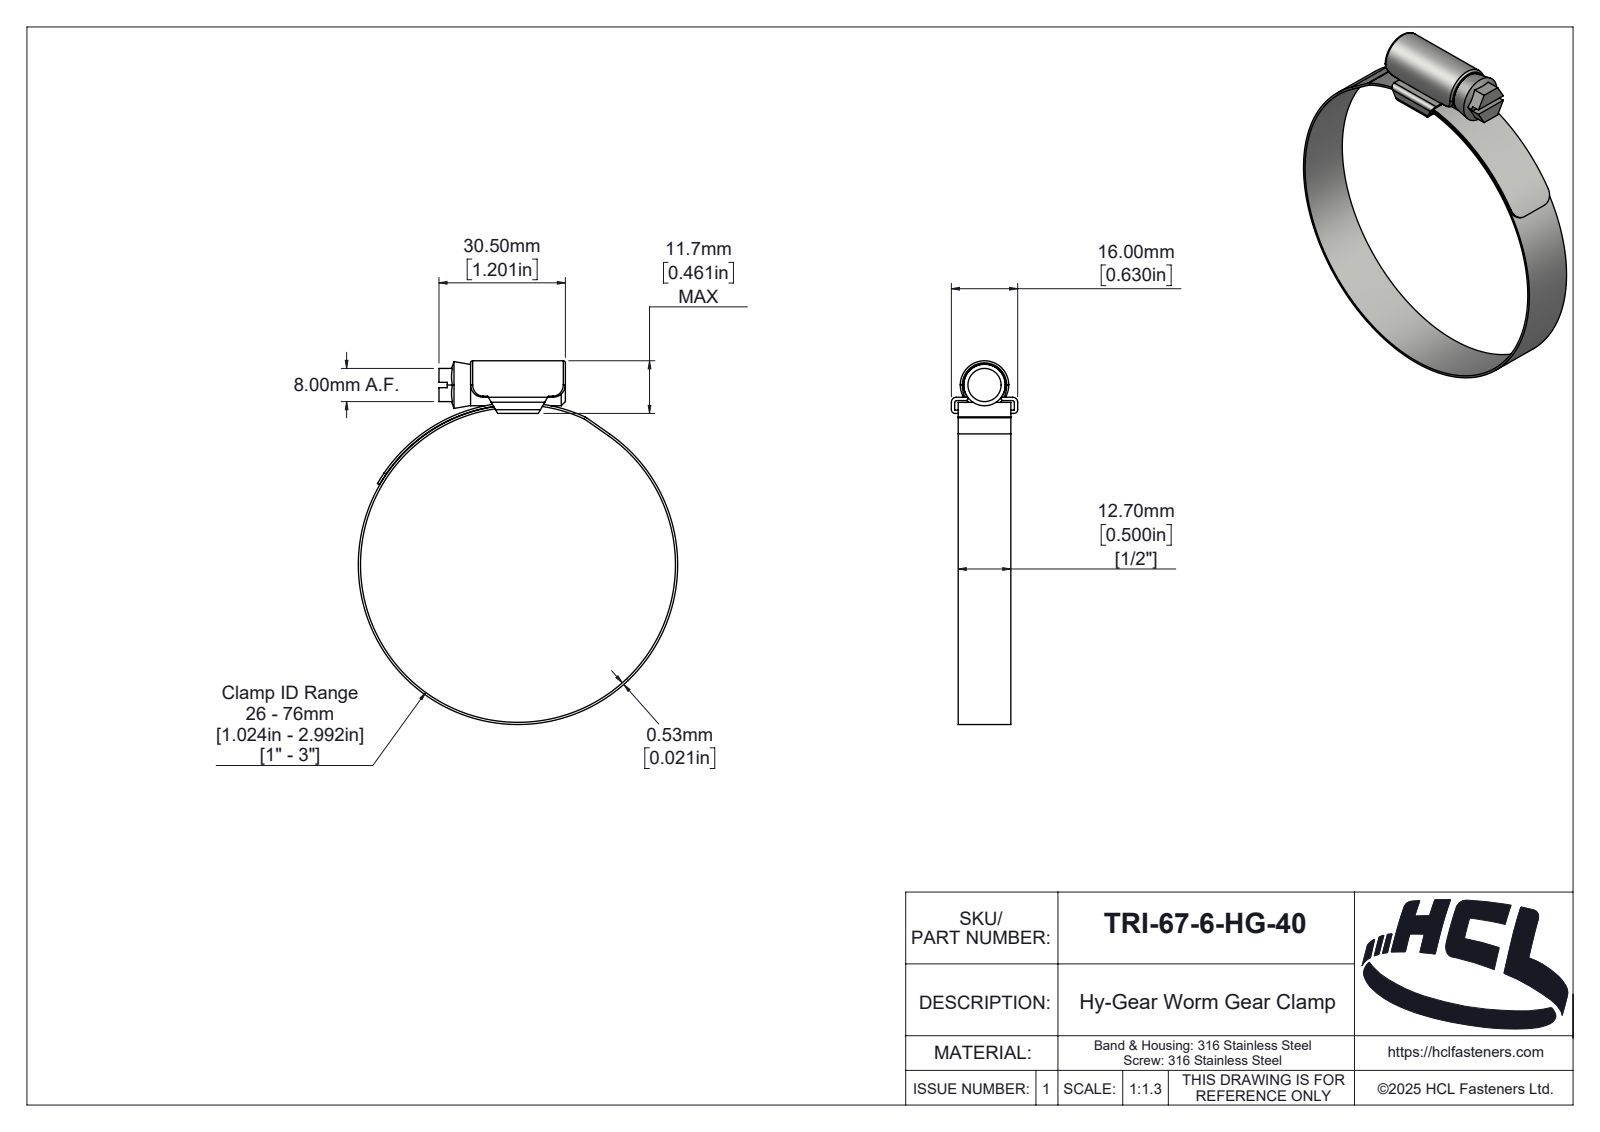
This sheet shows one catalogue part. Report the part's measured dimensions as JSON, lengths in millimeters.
{"part_name": "TRI-57-0-HG-40", "step_written_by": "SolidWorks 2025 (AUTOMOTIVE_DESIGN)", "units": "millimeters", "bodies": {"solids": 3, "faces": 189, "planar": 39, "cylindrical": 89, "other": 61}, "overall_size": [87.73, 77.06, 16], "volume_mm3": 4885, "surface_area_mm2": 10352, "round_holes": [[76, 1]], "round_bosses_or_shafts": [[77.06, 1], [10, 1]], "partial_cylinders_radius": [[0.5, 6], [3, 4], [0.1, 2], [0.9, 2], [1.2, 2], [0.46, 1], [1.89, 1], [2, 1]], "face_to_face_distances": [0.8, 12.7, 3.1, 0.53, 2.3, 3.9, 30.5, 1.65, 14.35, 15.2]}
